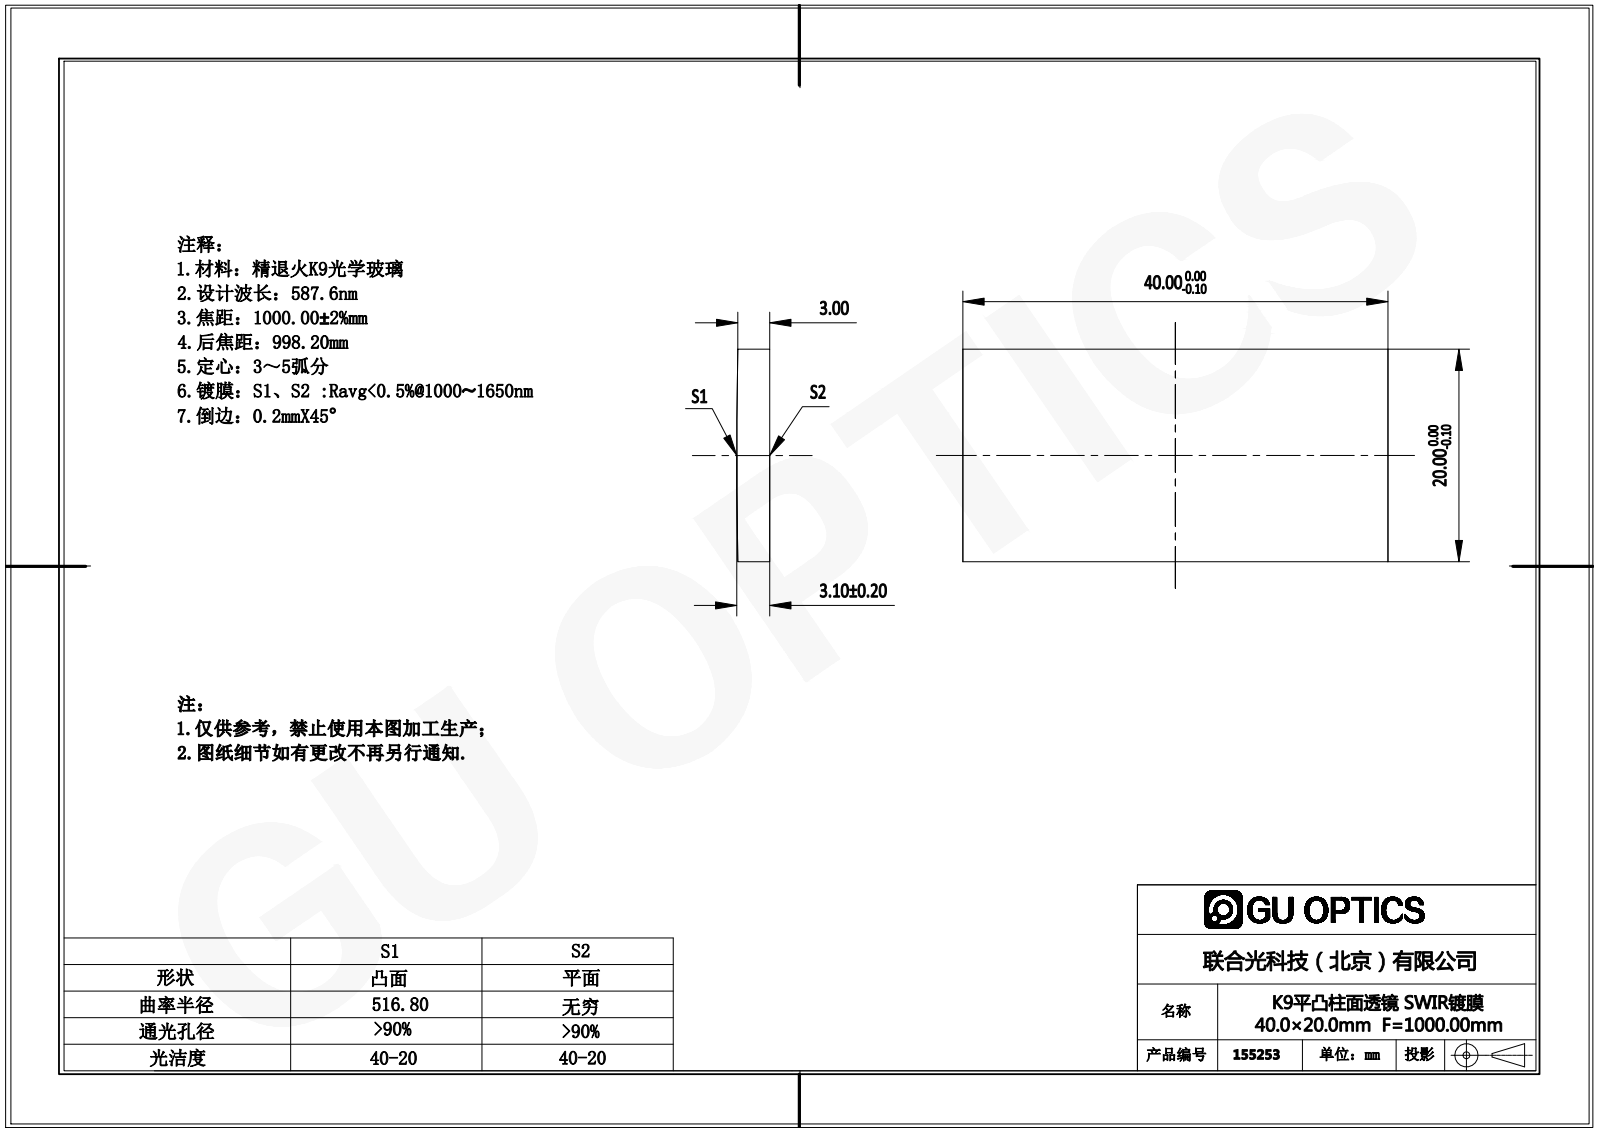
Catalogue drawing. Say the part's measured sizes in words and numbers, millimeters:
The part is named "155055". Its 3-D file was written by "SolidWorks 2016 (AUTOMOTIVE_DESIGN)". It is 1 solid with 6 faces: 5 planar, 1 cylindrical and 0 other. Overall it measures 40 by 20 by 3.1 millimeters. Its volume is 2 454 cubic millimeters and its surface area 1 963 square millimeters. Partial cylindrical surfaces (rounded edges, fillets, slot ends): 1 of radius 516.8. The main face-to-face distances are 20, 40.
